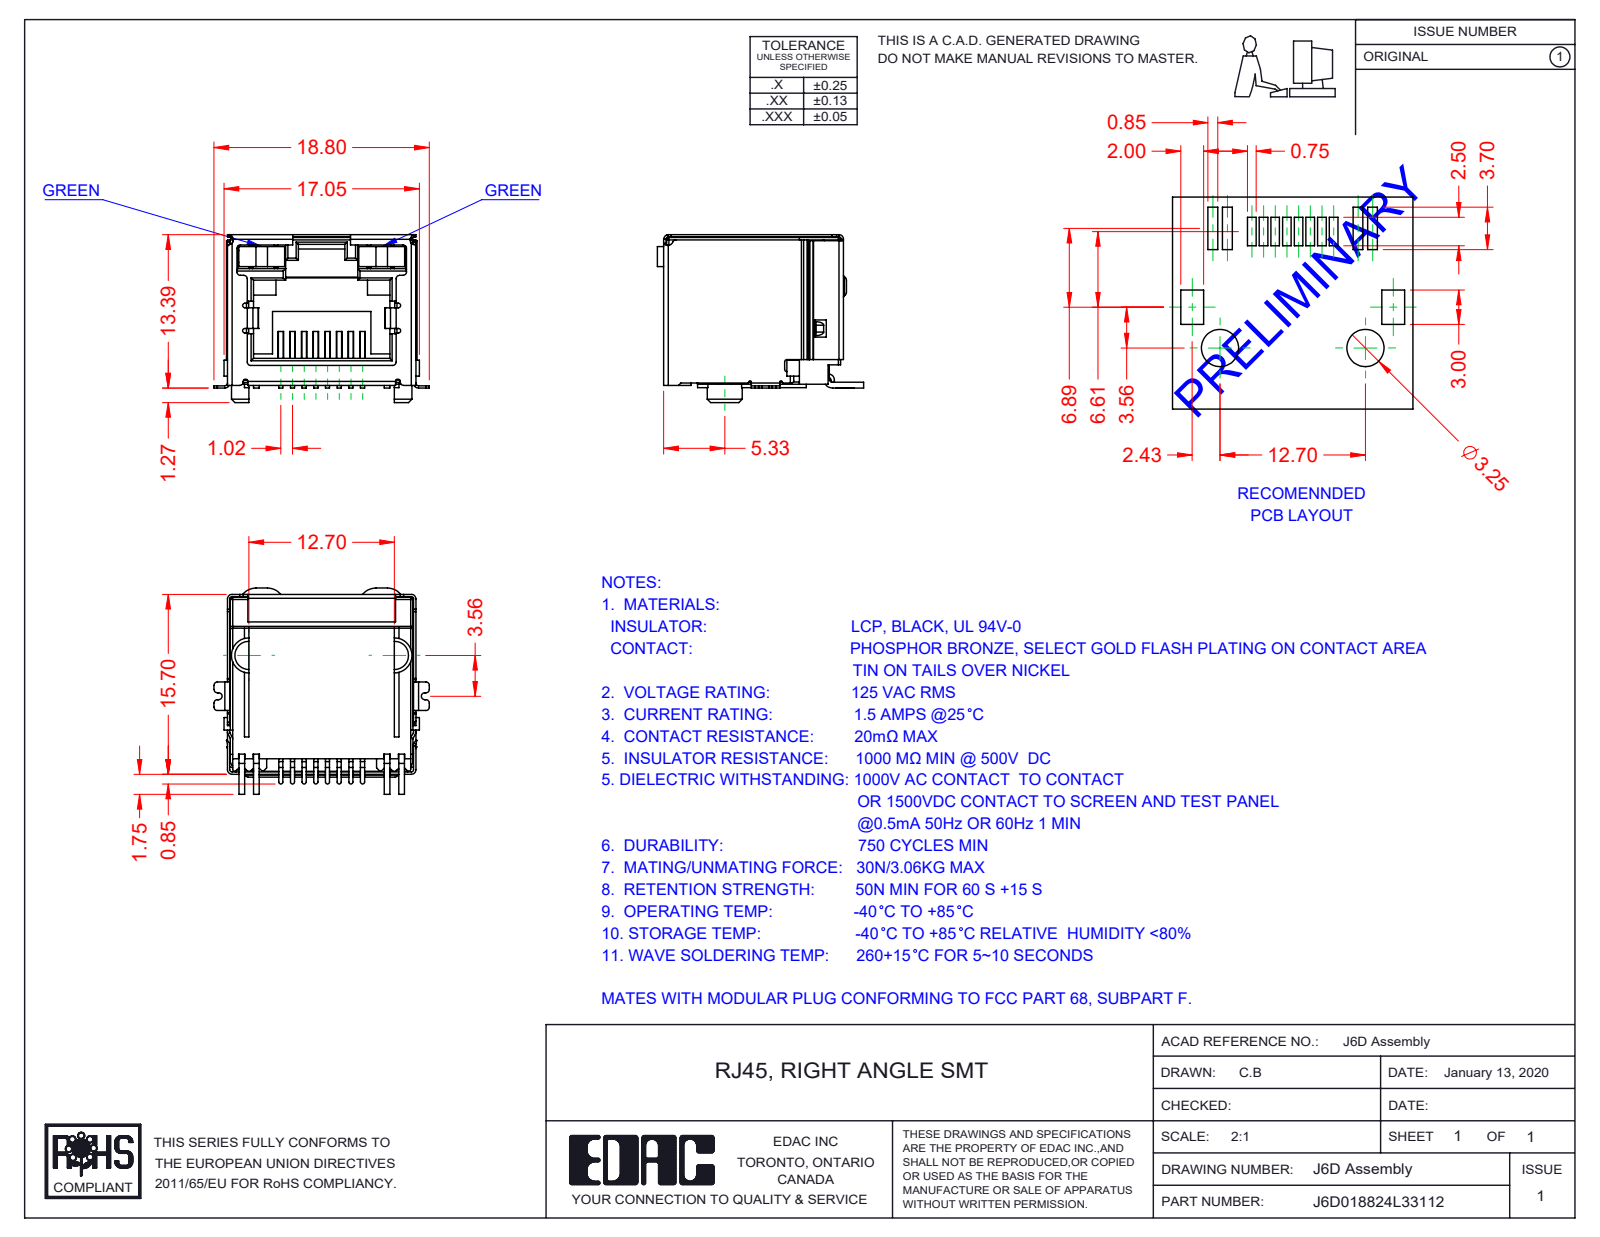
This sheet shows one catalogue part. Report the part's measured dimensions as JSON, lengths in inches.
{"part_name": "6D LED LH_3-Green; 6D LED RH_3-Green; 6D Shield_LED - No EMI; 6D Contacts (+2 more)", "step_written_by": "SolidWorks 2016 (CONFIG_CONTROL_DESIGN)", "units": "inches", "bodies": {"solids": 12, "faces": 893, "planar": 644, "cylindrical": 216, "other": 33}, "overall_size": [0.74, 0.709, 0.577], "volume_in3": 0.11, "surface_area_in2": 7.592, "partial_cylinders_radius": [[0.012, 39], [0.008, 37], [0.016, 16], [0.004, 12], [0.006, 8], [0.007, 8], [0.02, 6], [0.059, 5]], "face_to_face_distances": [0.63, 0.64, 0.638, 0.089, 0.039, 0.628, 0.632, 0.504, 0.018, 0.648]}
